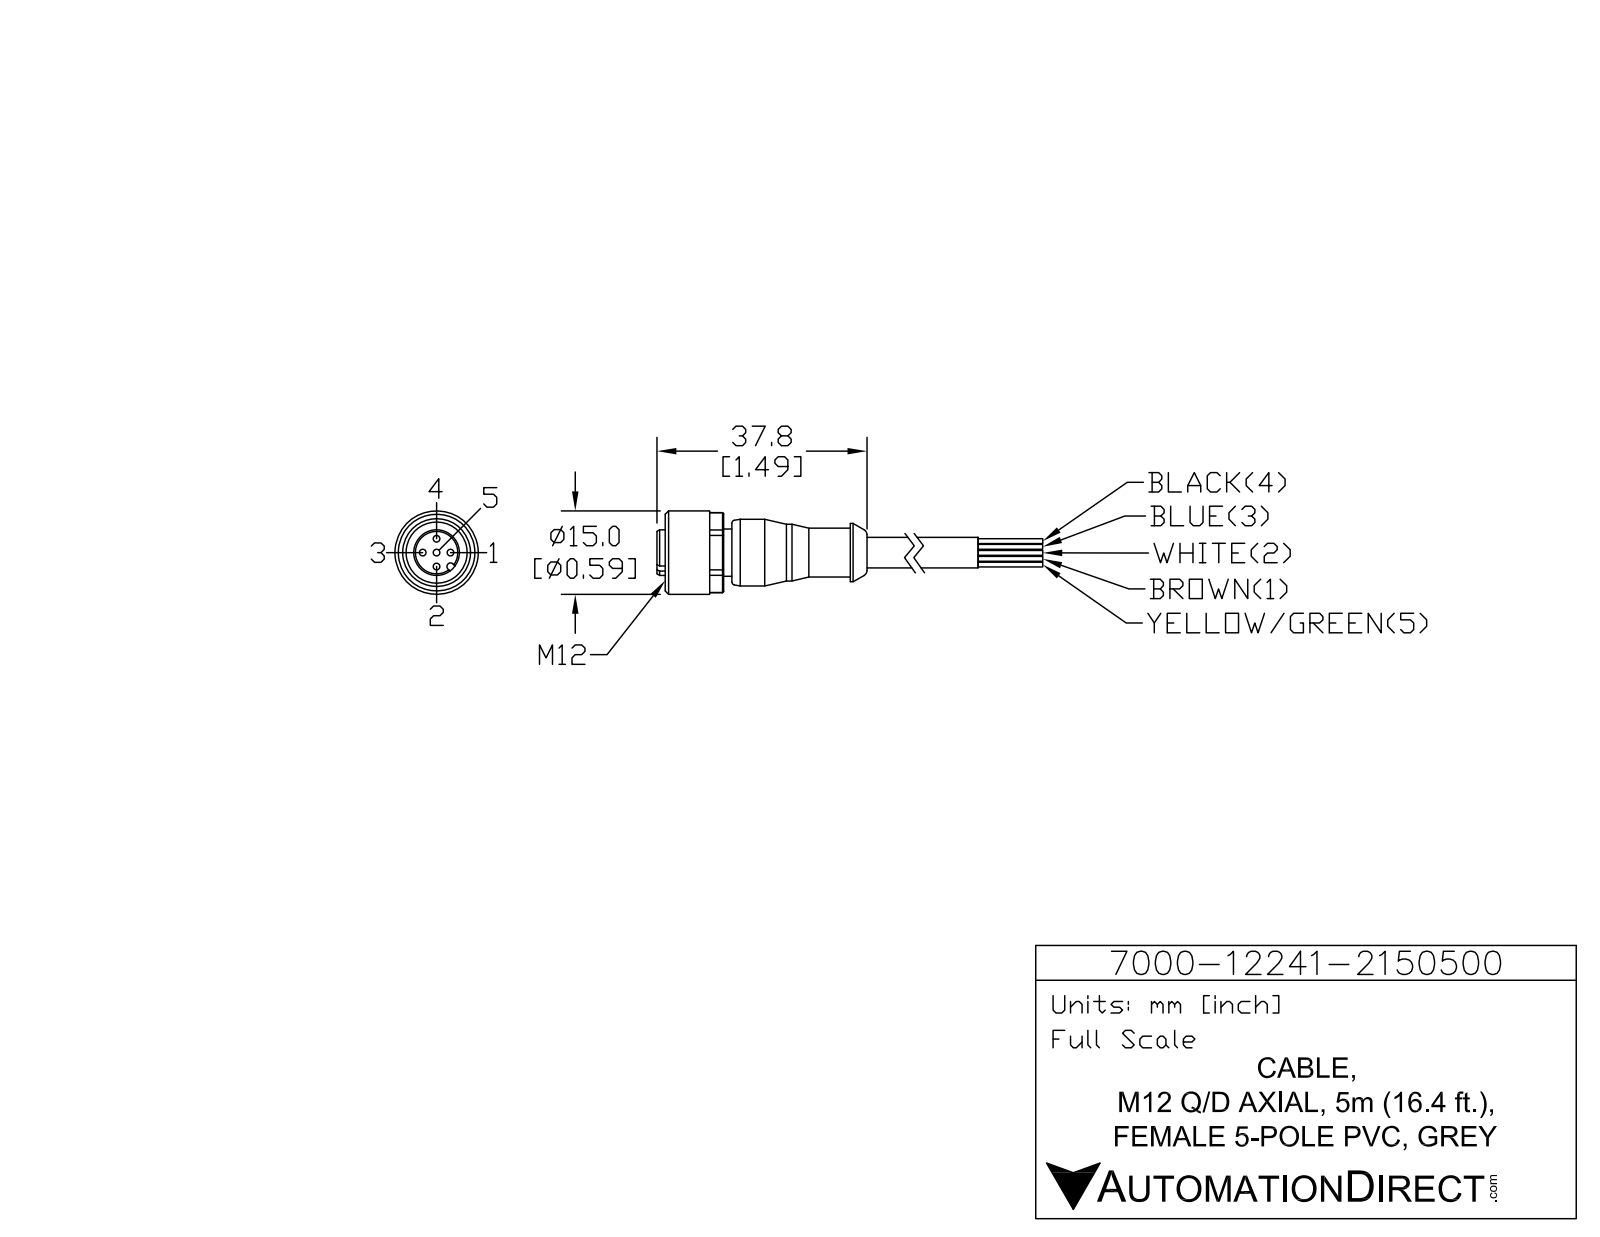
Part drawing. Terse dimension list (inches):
name: 7000-12241-2150500
written by: SolidWorks 2015 (AUTOMOTIVE_DESIGN)
unit: in
bodies: 1 solid, 93 faces (29 planar, 36 cylindrical, 28 other)
size: 2.276 × 0.591 × 0.591
volume: 0.246 in³; area: 4.134 in²
holes: 5× ⌀0.047, 1× ⌀0.433
bosses: 1× ⌀0.591, 1× ⌀0.472, 1× ⌀0.413, 1× ⌀0.402, 1× ⌀0.346, 1× ⌀0.335, 1× ⌀0.323, 1× ⌀0.217
rounds: 1× R0.026, 1× R0.283
face distances: 0.472, 0.059, 0.118, 0.512, 0.354, 1.016, 0.295, 0.413, 0.098, 0.531
hole spacings: 0.098, 0.139, 0.197
